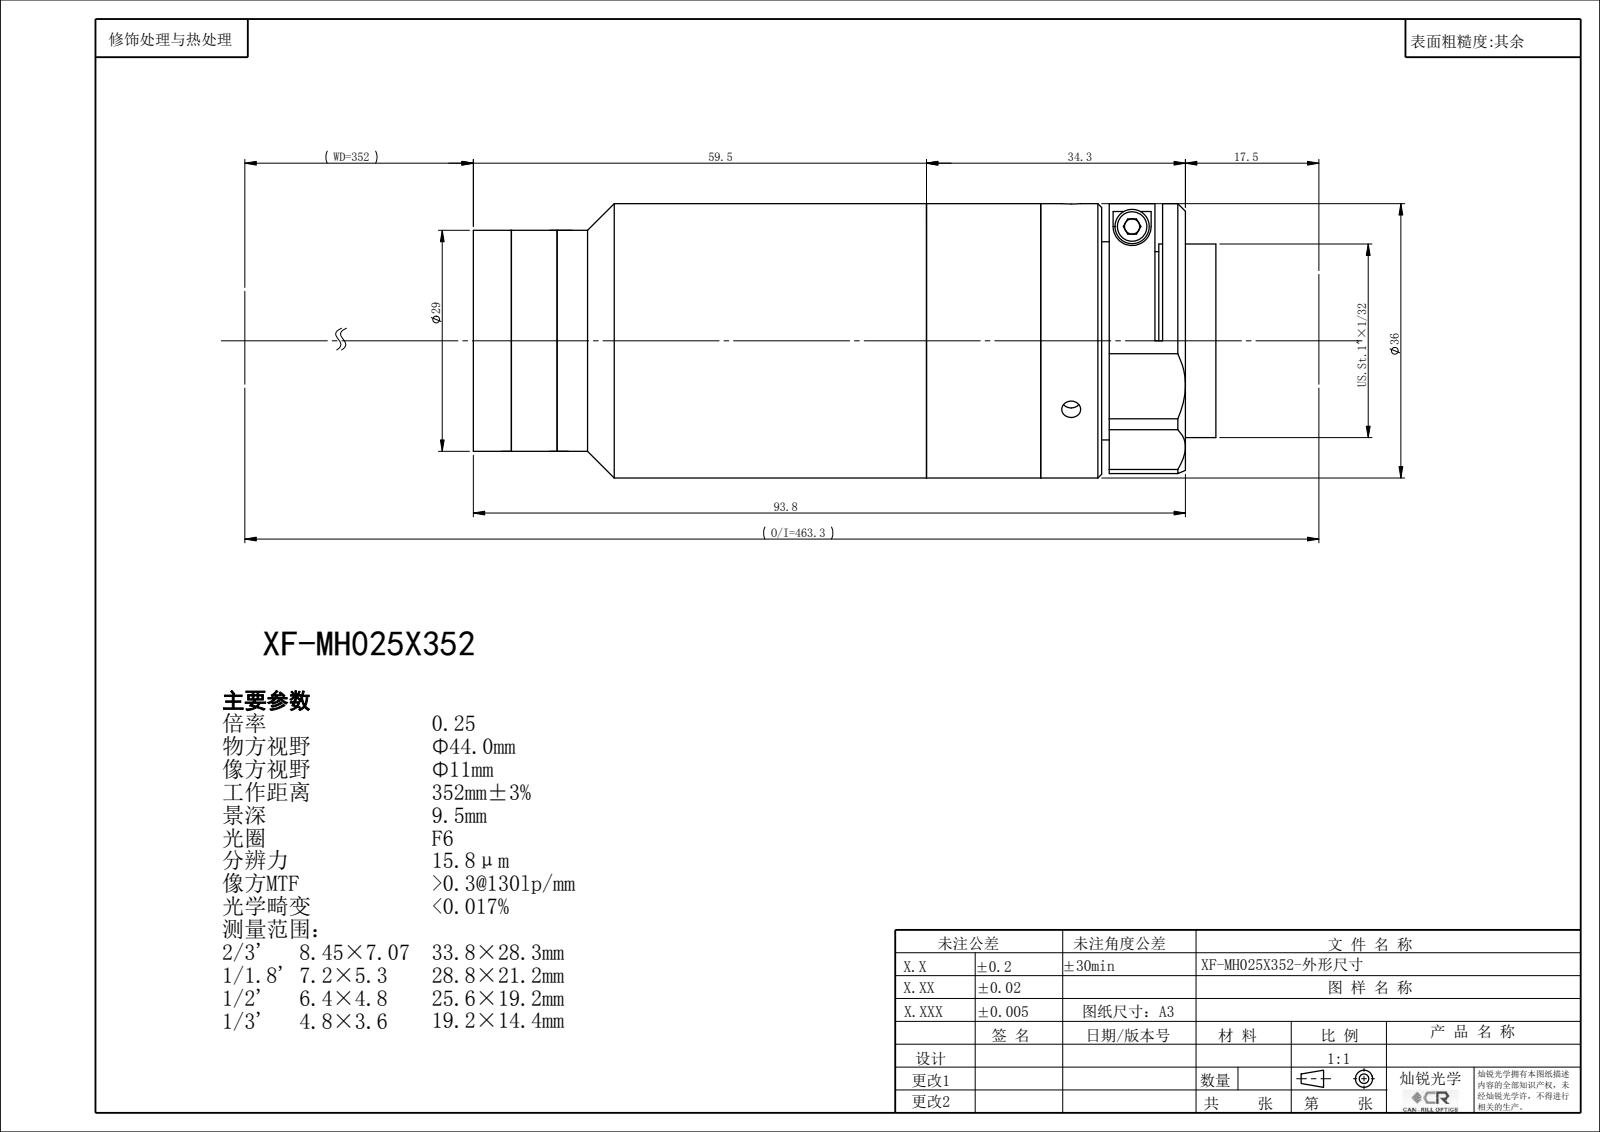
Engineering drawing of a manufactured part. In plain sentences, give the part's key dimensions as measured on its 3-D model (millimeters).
The part is named "XF-MH025X352". Its 3-D file was written by "SolidWorks 2022 (CONFIG_CONTROL_DESIGN)". It is 0 solids with 124 faces: 62 planar, 40 cylindrical and 22 other. Overall it measures 101.78 by 36 by 36 millimeters. Round holes: 3 of diameter 2.5, 1 of diameter 18, 1 of diameter 22.4, 1 of diameter 24, 1 of diameter 24.9, 1 of diameter 26.4. Round bosses or shafts: 1 of diameter 36, 1 of diameter 34, 1 of diameter 29, 1 of diameter 25.4. The main face-to-face distances are 19.28, 1.5, 17.78, 19, 36.78, 38.28, 92.78, 56, 75, 94.28.
